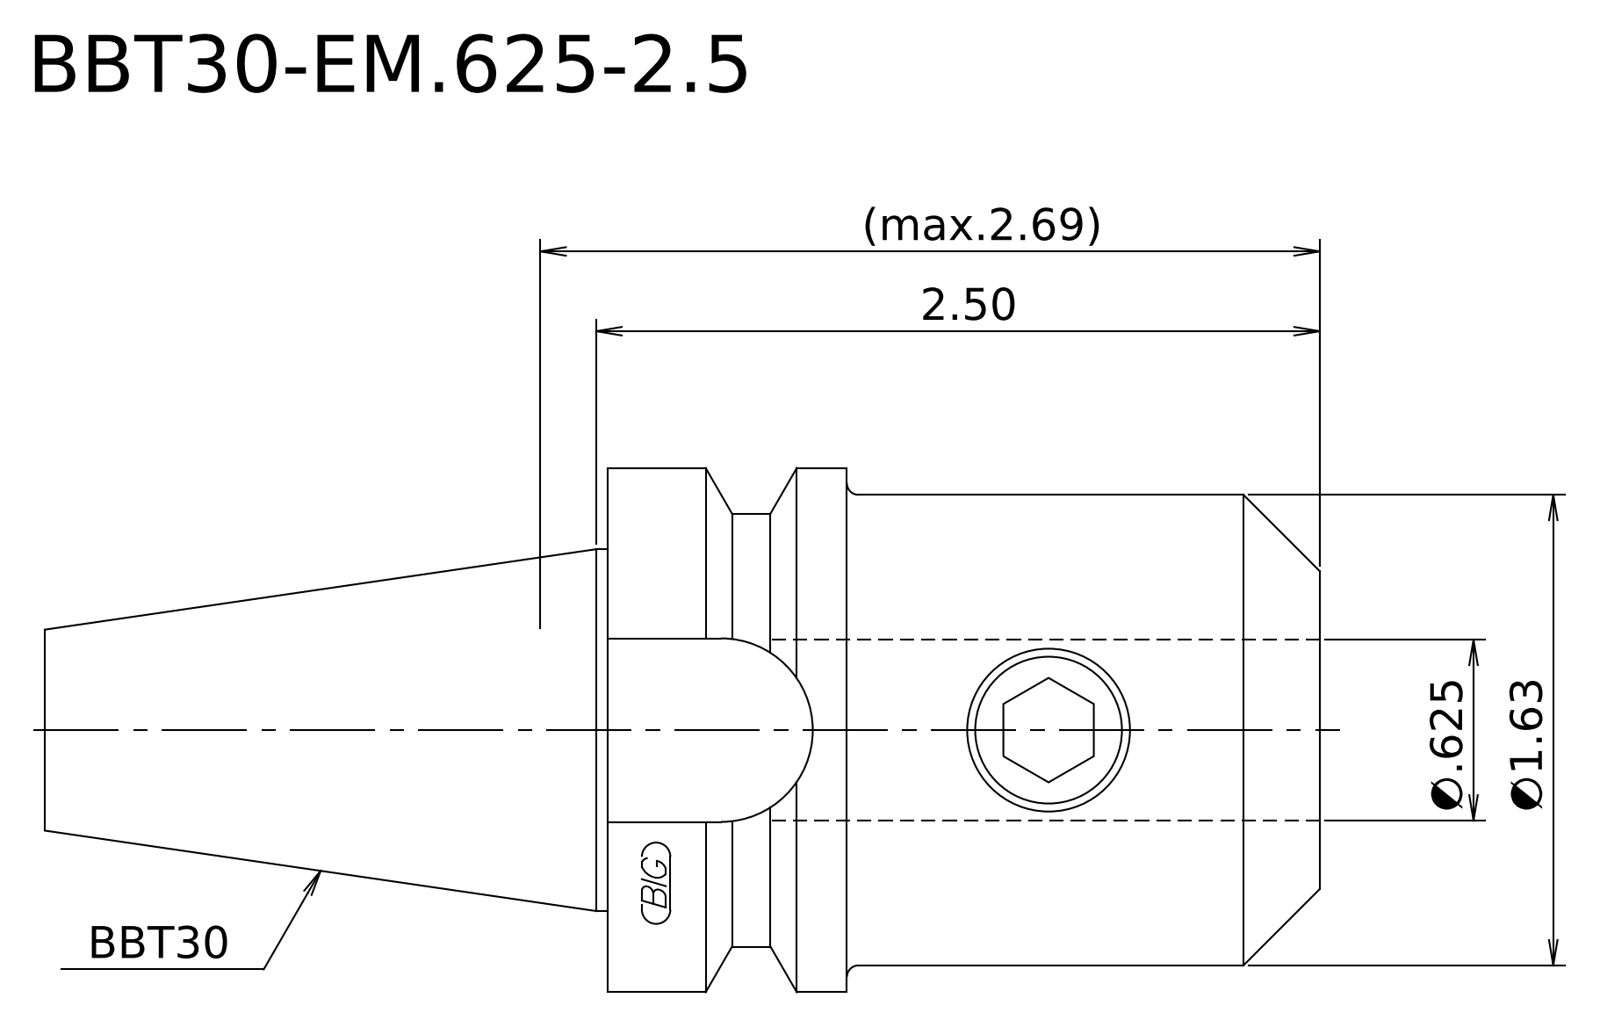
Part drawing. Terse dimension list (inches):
name: BBT30-EM_625-2_5
written by: SolidWorks 2021 (CONFIG_CONTROL_DESIGN)
unit: in
bodies: 1 solid, 27 faces (7 planar, 12 cylindrical, 8 other)
size: 4.406 × 1.811 × 1.811
volume: 6.169 in³; area: 26.72 in²
holes: 1× ⌀0.625
bosses: 1× ⌀1.811, 1× ⌀1.625, 1× ⌀1.496, 1× ⌀1.25
face distances: 0.807, 1.673, 2.48, 4.406, 2.732, 1.925, 1.866, 1.984, 0.193, 0.311
